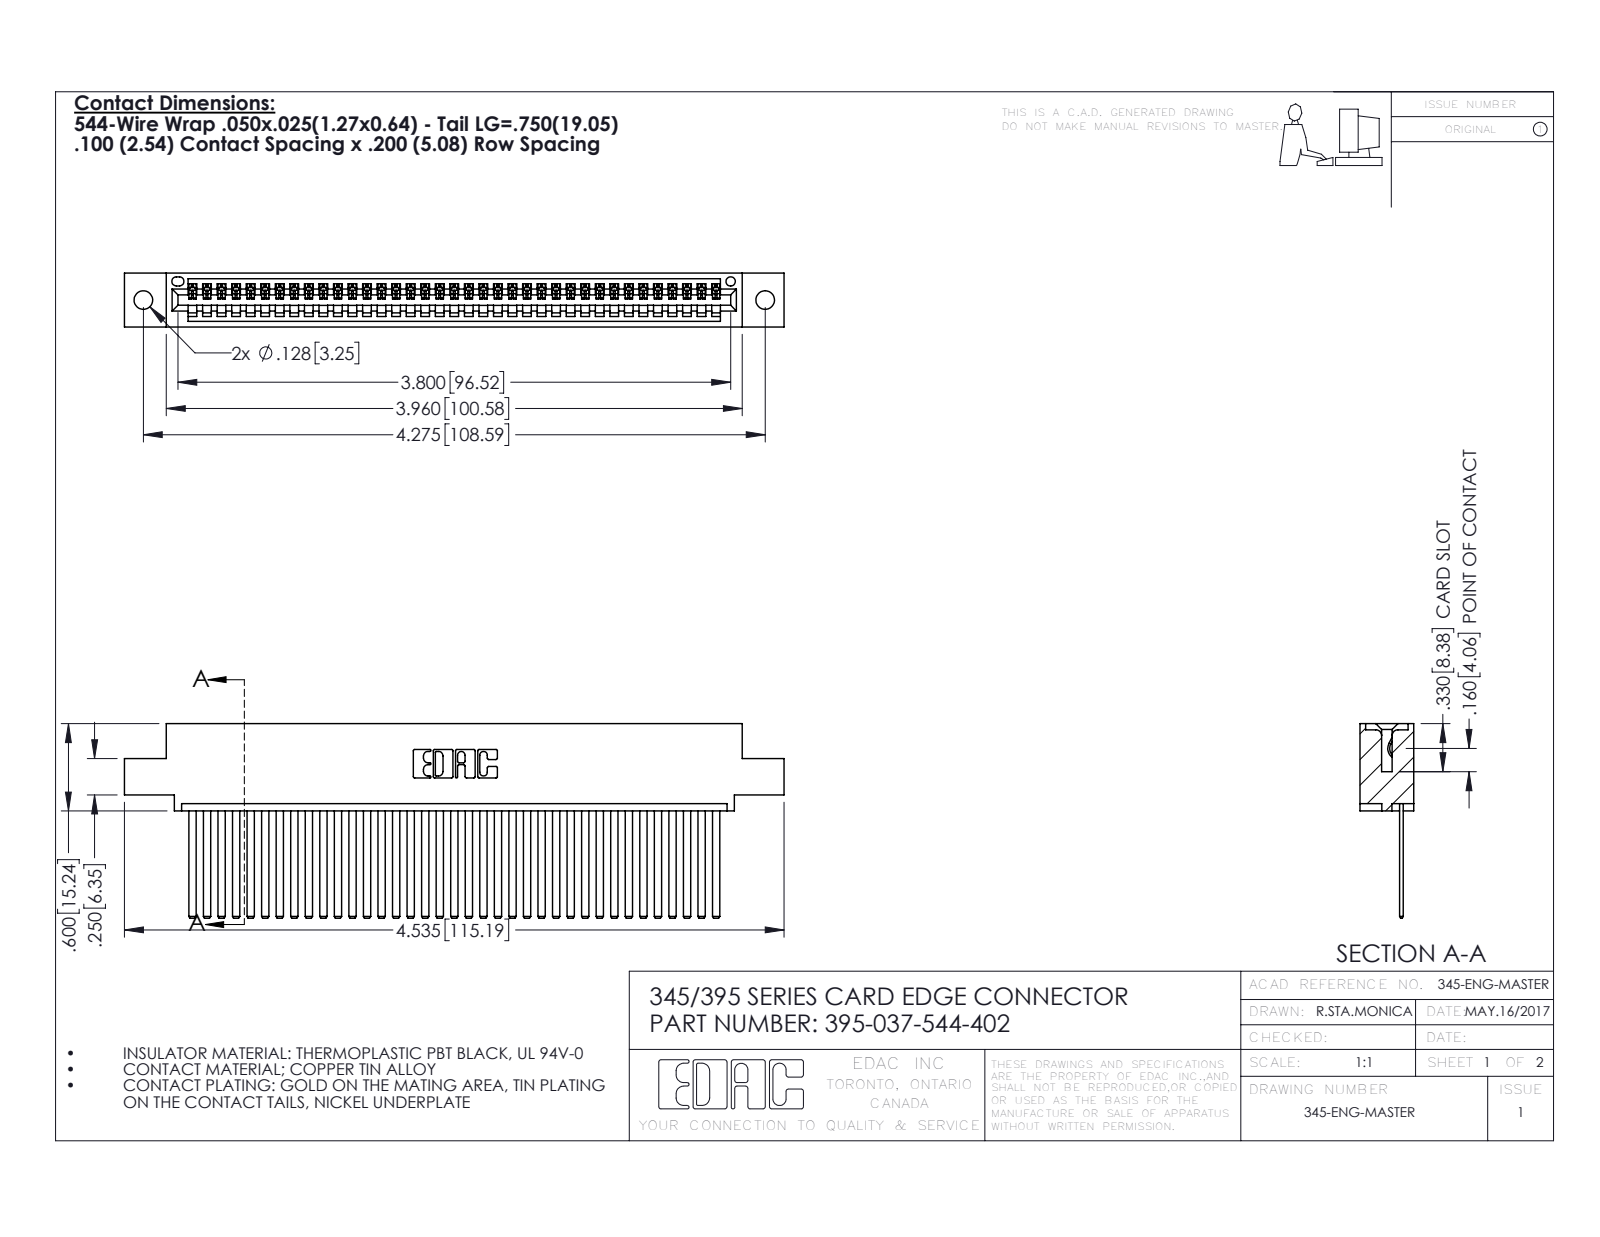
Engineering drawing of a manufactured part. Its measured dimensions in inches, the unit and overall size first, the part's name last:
Units: inches
Overall size (bounding box): 4.535 × 1.337 × 0.37
Round holes (diameter × count): ⌀0.128 ×2, ⌀0.064 ×1
Partial cylindrical surfaces — rounded edges, fillets, slot ends (radius × count): R0.006 ×74, R0.01 ×22, R0.007 ×6, R0.031 ×6, R0.026 ×3, R0.031 ×2, R0.04 ×2, R0.014 ×1
Main face-to-face distances: 0.072, 0.298, 0.025, 0.098, 0.272, 0.37, 0.2, 0.225, 0.149, 0.072
Hole centre spacings: 0.27, 4.039, 4.275
Volume: 0.685 in³ · Surface area: 24.7 in²
Bodies: 38 solids, 2054 faces (1416 planar, 638 cylindrical, 0 other)
Part name (STEP PRODUCT): 395-037-544-402; 345-292-001_345-293-144; 345 Part_0.110 Offset - 0.128 Dia
STEP written by: SolidWorks 2016 (CONFIG_CONTROL_DESIGN)
